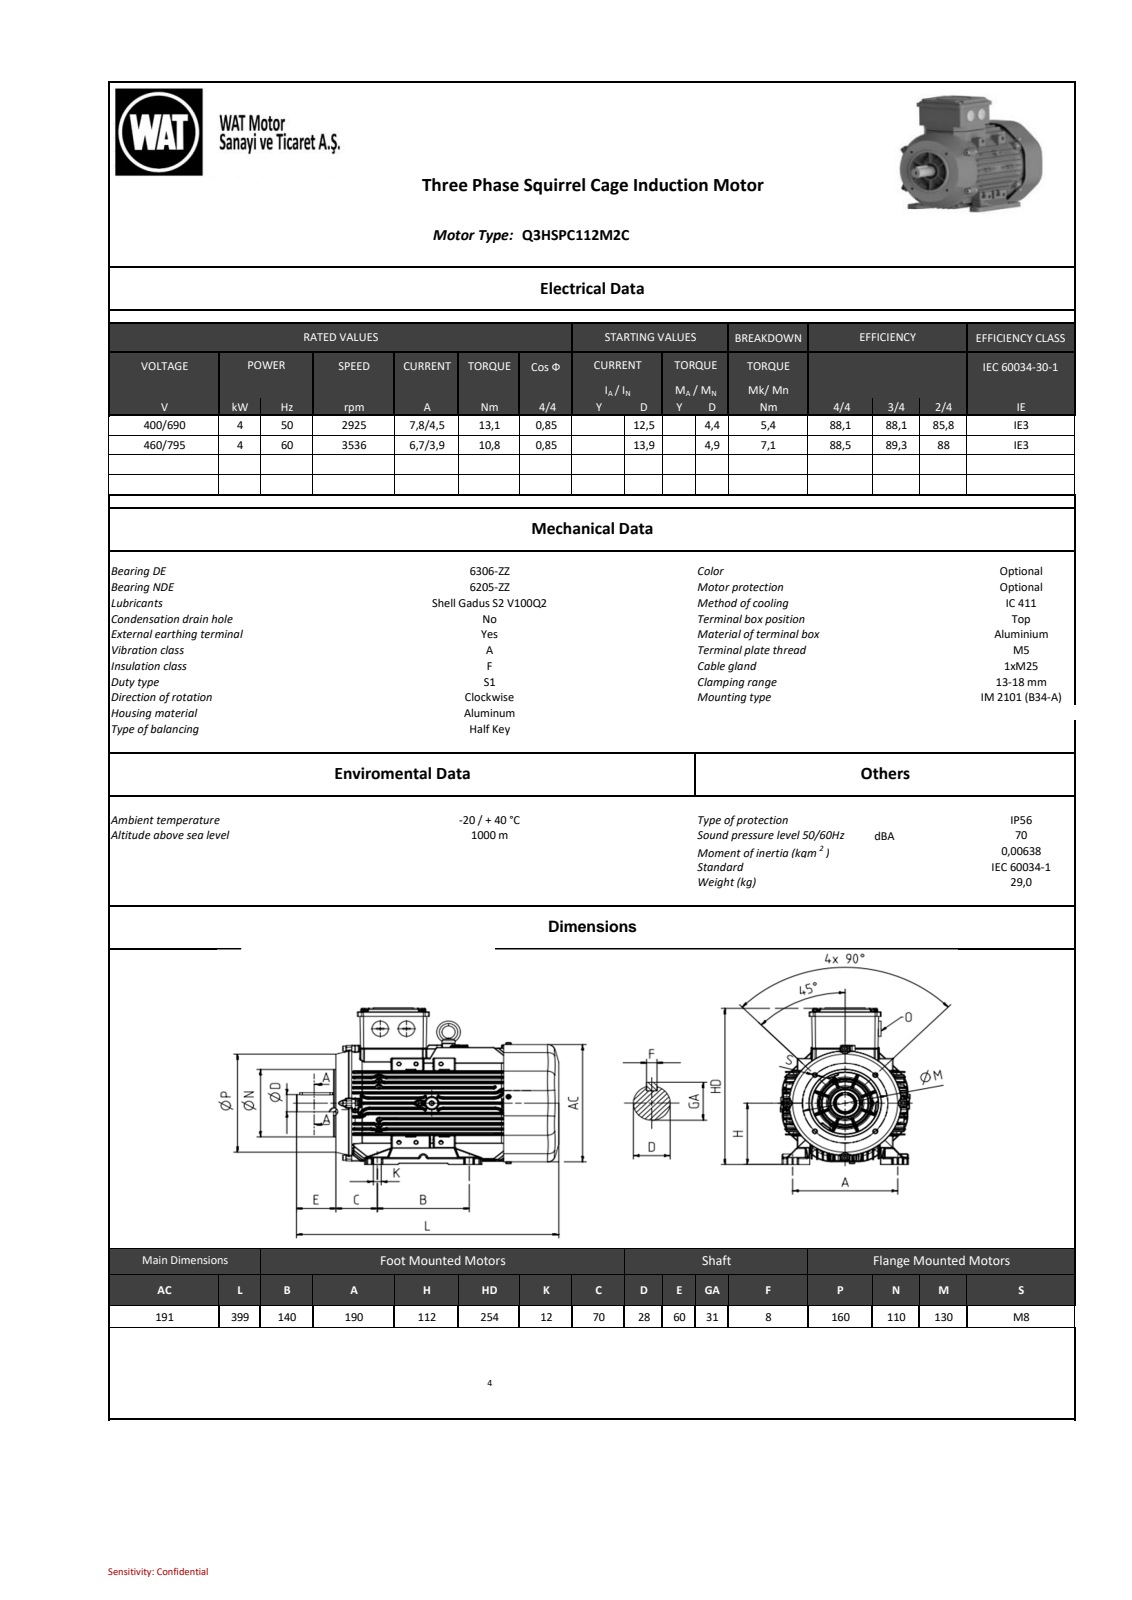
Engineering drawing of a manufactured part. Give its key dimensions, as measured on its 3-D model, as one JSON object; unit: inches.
{"part_name": "QHS Series_ 112_B34a_stp_objects", "step_written_by": "SIEMENS PLM Software NX2206.8101 (AUTOMOTIVE_DESIGN)", "units": "inches", "bodies": {"solids": 0, "faces": 6745, "planar": 1536, "cylindrical": 2759, "other": 2450}, "overall_size": [15.721, 10.048, 8.737], "round_holes": [[0.268, 4], [0.394, 1], [1.749, 1], [2.26, 1], [3.504, 1], [4.291, 1], [5.079, 1], [5.236, 1]], "round_bosses_or_shafts": [[0.315, 8], [0.366, 4], [0.335, 4], [0.197, 4], [0.984, 3], [4.469, 1], [4.331, 1], [3.681, 1]], "partial_cylinders_radius": [[0.039, 723], [0.031, 661], [0.03, 108], [0.079, 93], [0.02, 81], [0.032, 51], [0.197, 44], [0.591, 26]], "face_to_face_distances": [0.336, 0.333, 0.333, 3.002, 0.666, 3.679, 3.019, 0.671, 1.007, 2.348], "hole_center_spacings": [2.559, 3.619, 5.118]}
